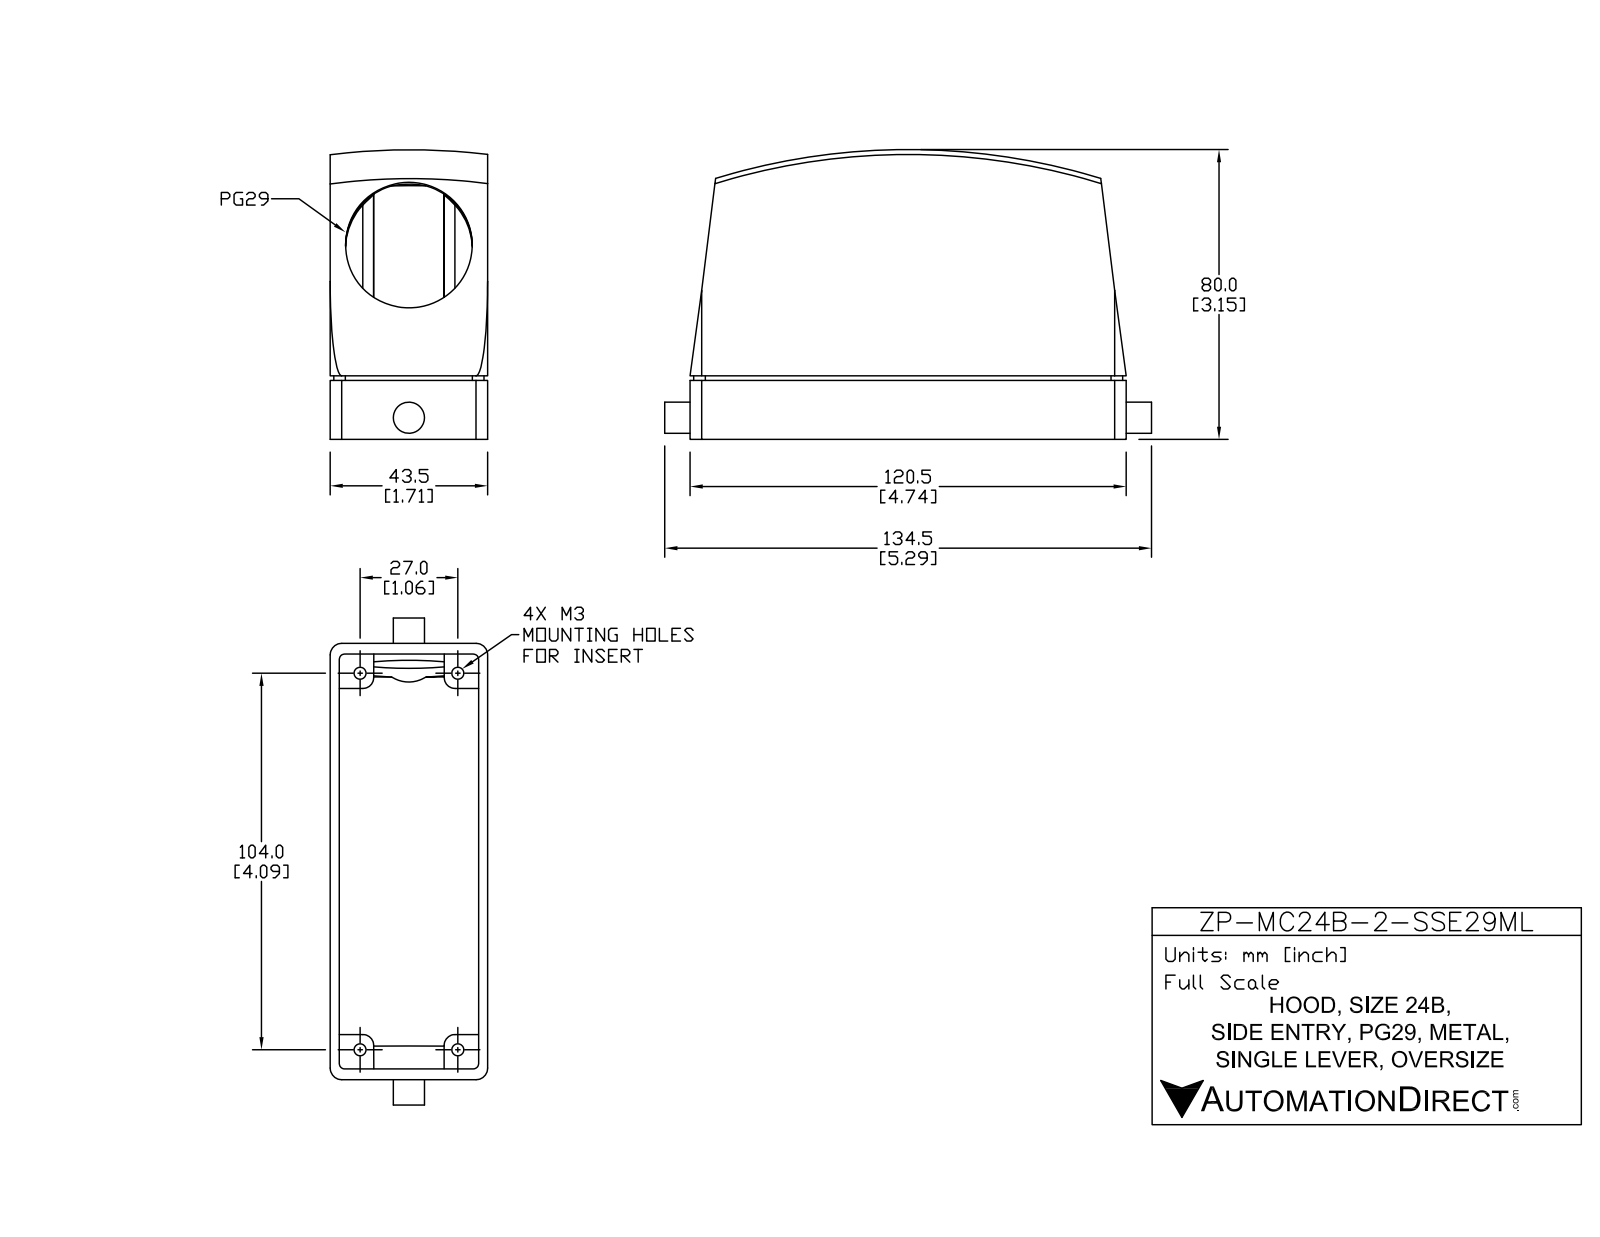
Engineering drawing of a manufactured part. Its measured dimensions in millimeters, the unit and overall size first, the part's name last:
Units: millimetres
Overall size (bounding box): 134.5 × 77.55 × 43.5
Round holes (diameter × count): ⌀3.3 ×4, ⌀35 ×1
Round bosses / shafts (diameter × count): ⌀8.6 ×1
Partial cylindrical surfaces — rounded edges, fillets, slot ends (radius × count): R3.2 ×8, R1.5 ×4, R3 ×4, R0.7 ×1
Main face-to-face distances: 2.5, 41, 43.5, 38.5, 9.5, 105.08, 2.96, 12.46, 108.04, 117.54
Hole centre spacings: 27, 104, 107.45
Volume: 77 322 mm³ · Surface area: 60 346 mm²
Bodies: 5 solids, 92 faces (54 planar, 32 cylindrical, 6 other)
Part name (STEP PRODUCT): ZP-MC24B-2-SSE29ML
STEP written by: SolidWorks 2011 (AUTOMOTIVE_DESIGN)
